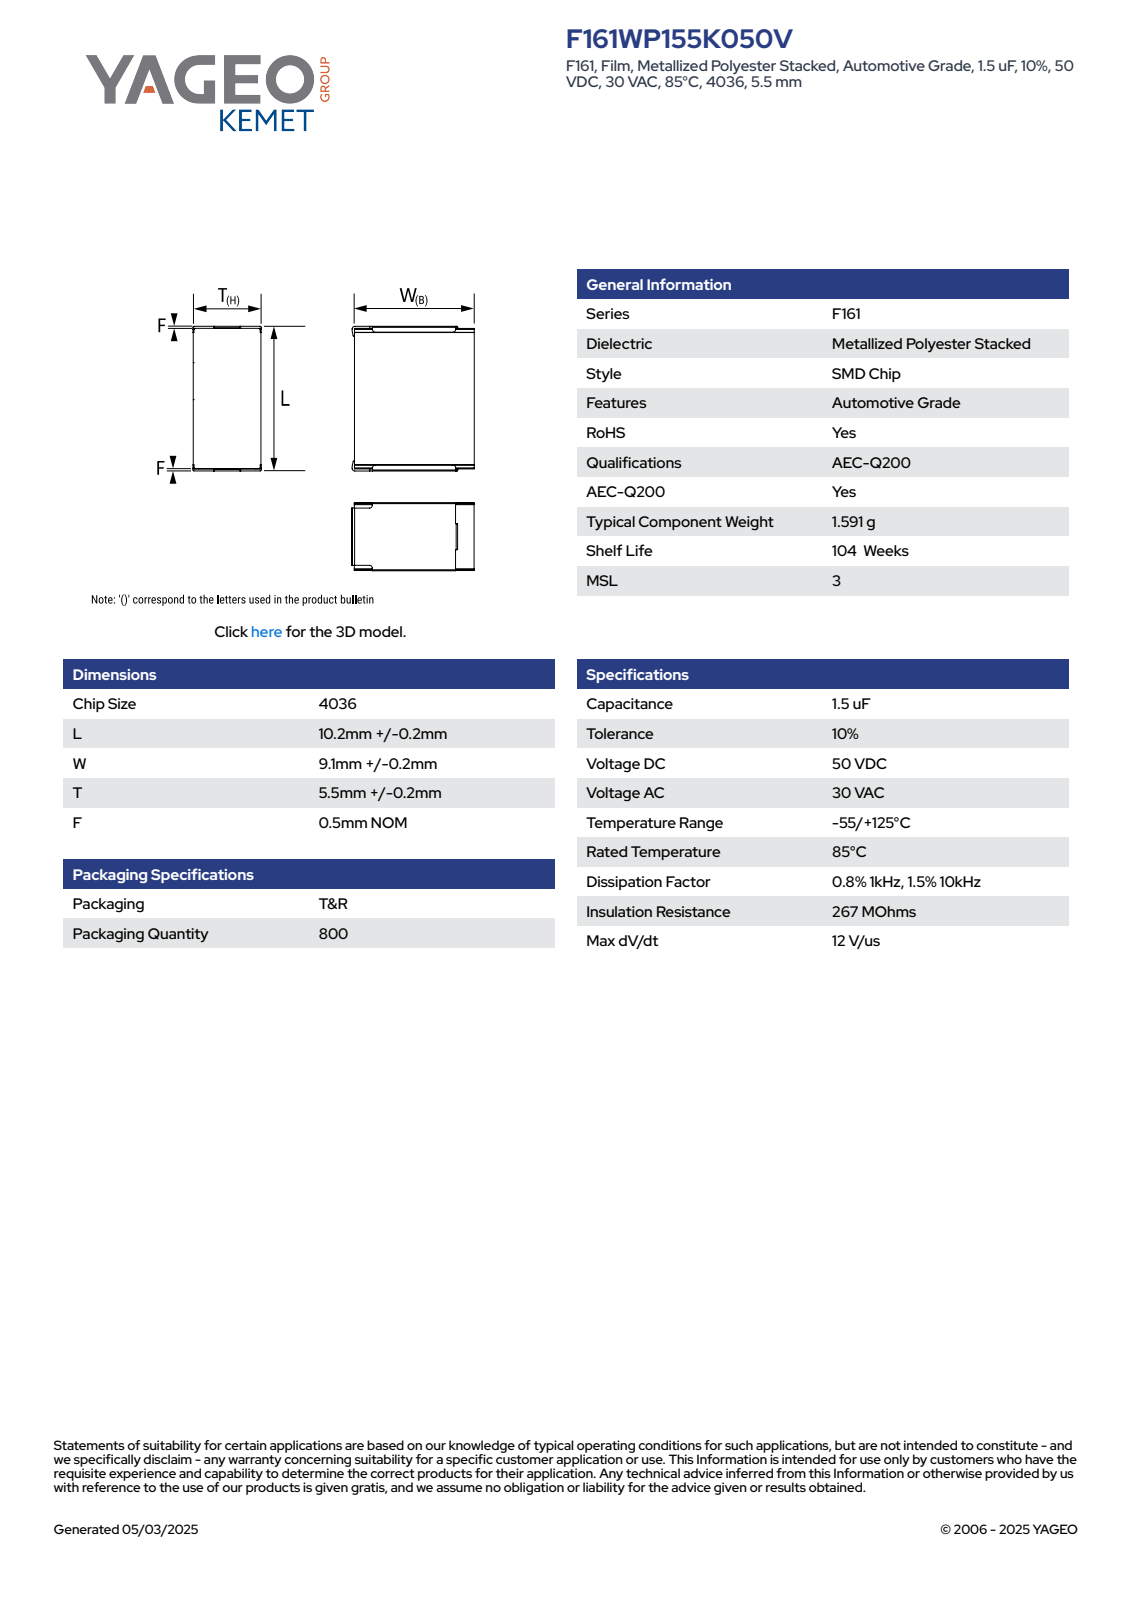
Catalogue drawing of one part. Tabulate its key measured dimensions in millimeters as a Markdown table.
| quantity | value |
| --- | --- |
| part name | CFS_KSTD_4036_L10.4W9.3T5.7F0.5 |
| STEP written by | SolidWorks 2021 (AUTOMOTIVE_DESIGN) |
| units | millimeters |
| bodies | 4 solids, 117 faces (103 planar, 14 cylindrical, 0 other) |
| overall size | 10.4 × 9.61 × 5.99 |
| volume | 530 mm³ |
| surface area | 440 mm² |
| partial cylindrical surfaces (radius × count) | 0.34 × 10, 0.36 × 4 |
| main face-to-face distances | 5.7, 8.93, 10.4, 0.5, 9.9, 5.85, 9.4, 0.37, 0.68, 0.31 |
